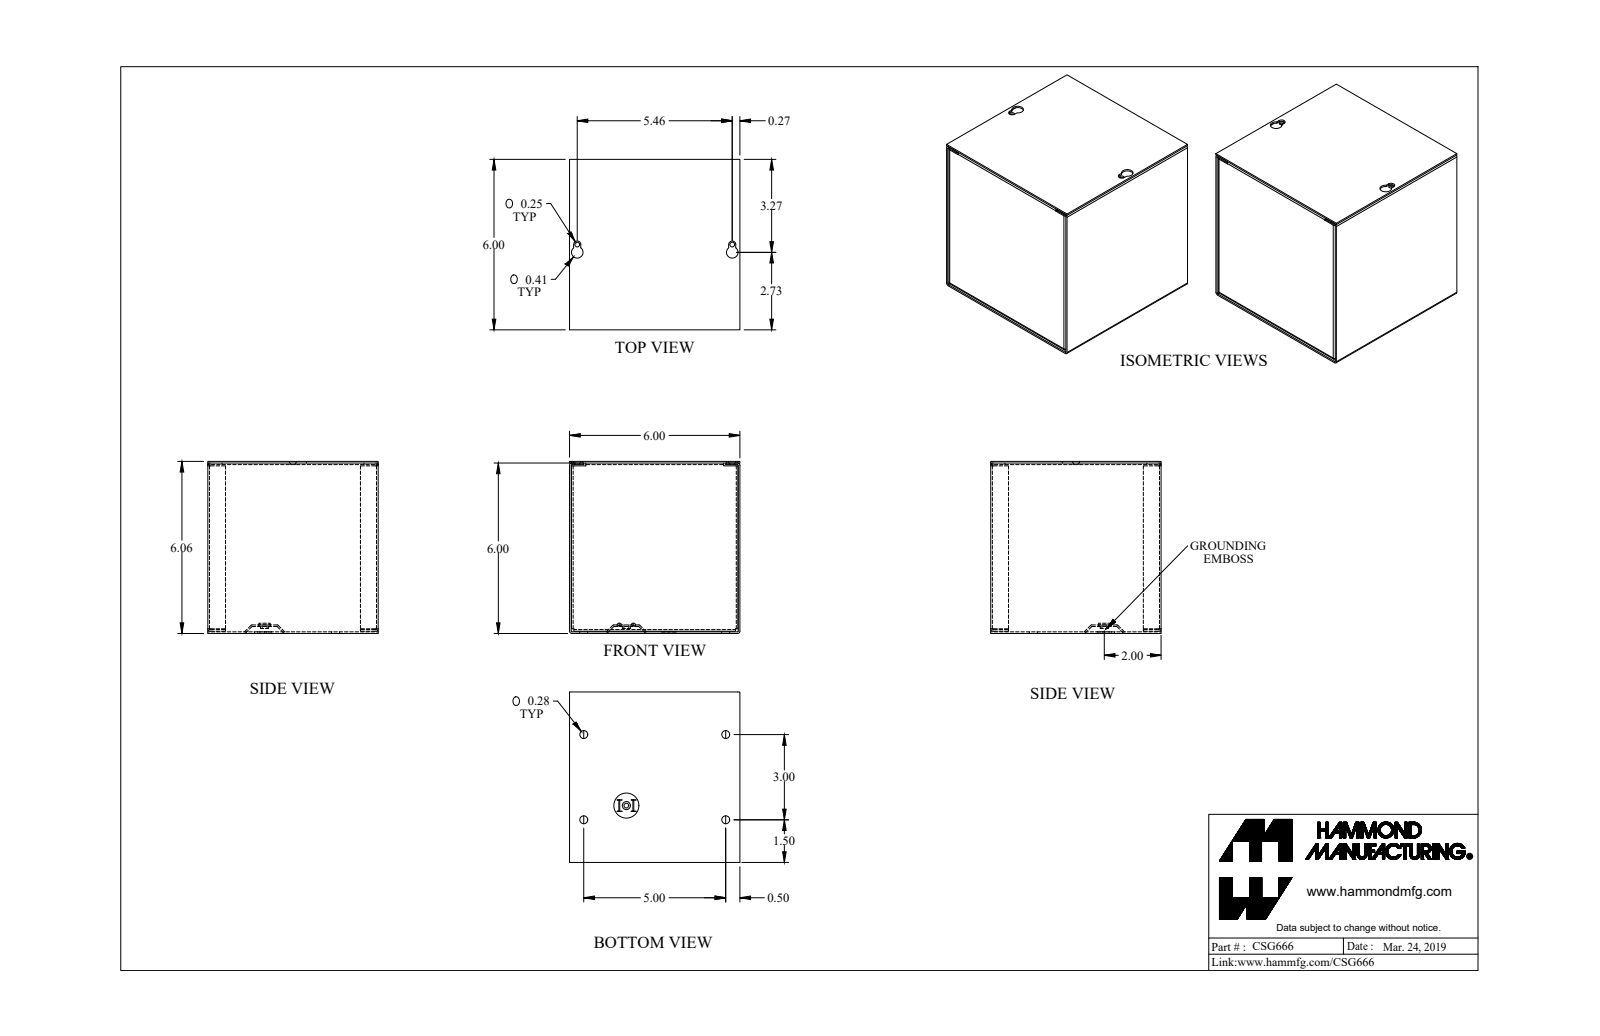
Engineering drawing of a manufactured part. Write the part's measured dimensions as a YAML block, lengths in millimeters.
part_name: "CSG666_Default"
step_written_by: "SolidWorks 2019 (CONFIG_CONTROL_DESIGN)"
units: millimeters
bodies: {solids: 4, faces: 189, planar: 121, cylindrical: 60, other: 8}
overall_size: [153.8, 152.4, 152.4]
volume: 223800
surface_area: 314400
round_holes:
  - {diameter: 7.1, count: 4}
  - {diameter: 4.3, count: 3}
  - {diameter: 12.7, count: 1}
round_bosses_or_shafts:
  - {diameter: 12.5, count: 1}
  - {diameter: 7.2, count: 1}
partial_cylinders:
  - {radius: 0.7, count: 12}
  - {radius: 2.2, count: 12}
  - {radius: 1.4, count: 8}
  - {radius: 3.2, count: 2}
  - {radius: 5.2, count: 2}
face_to_face_distances: [1.4, 151, 152.4, 149.5, 153.8, 1.8, 149.2, 3.2, 147.7, 150.6]
hole_center_spacings: [38.5, 138.2, 76.2, 127, 148.1, 38.1, 40.2, 50.7]
